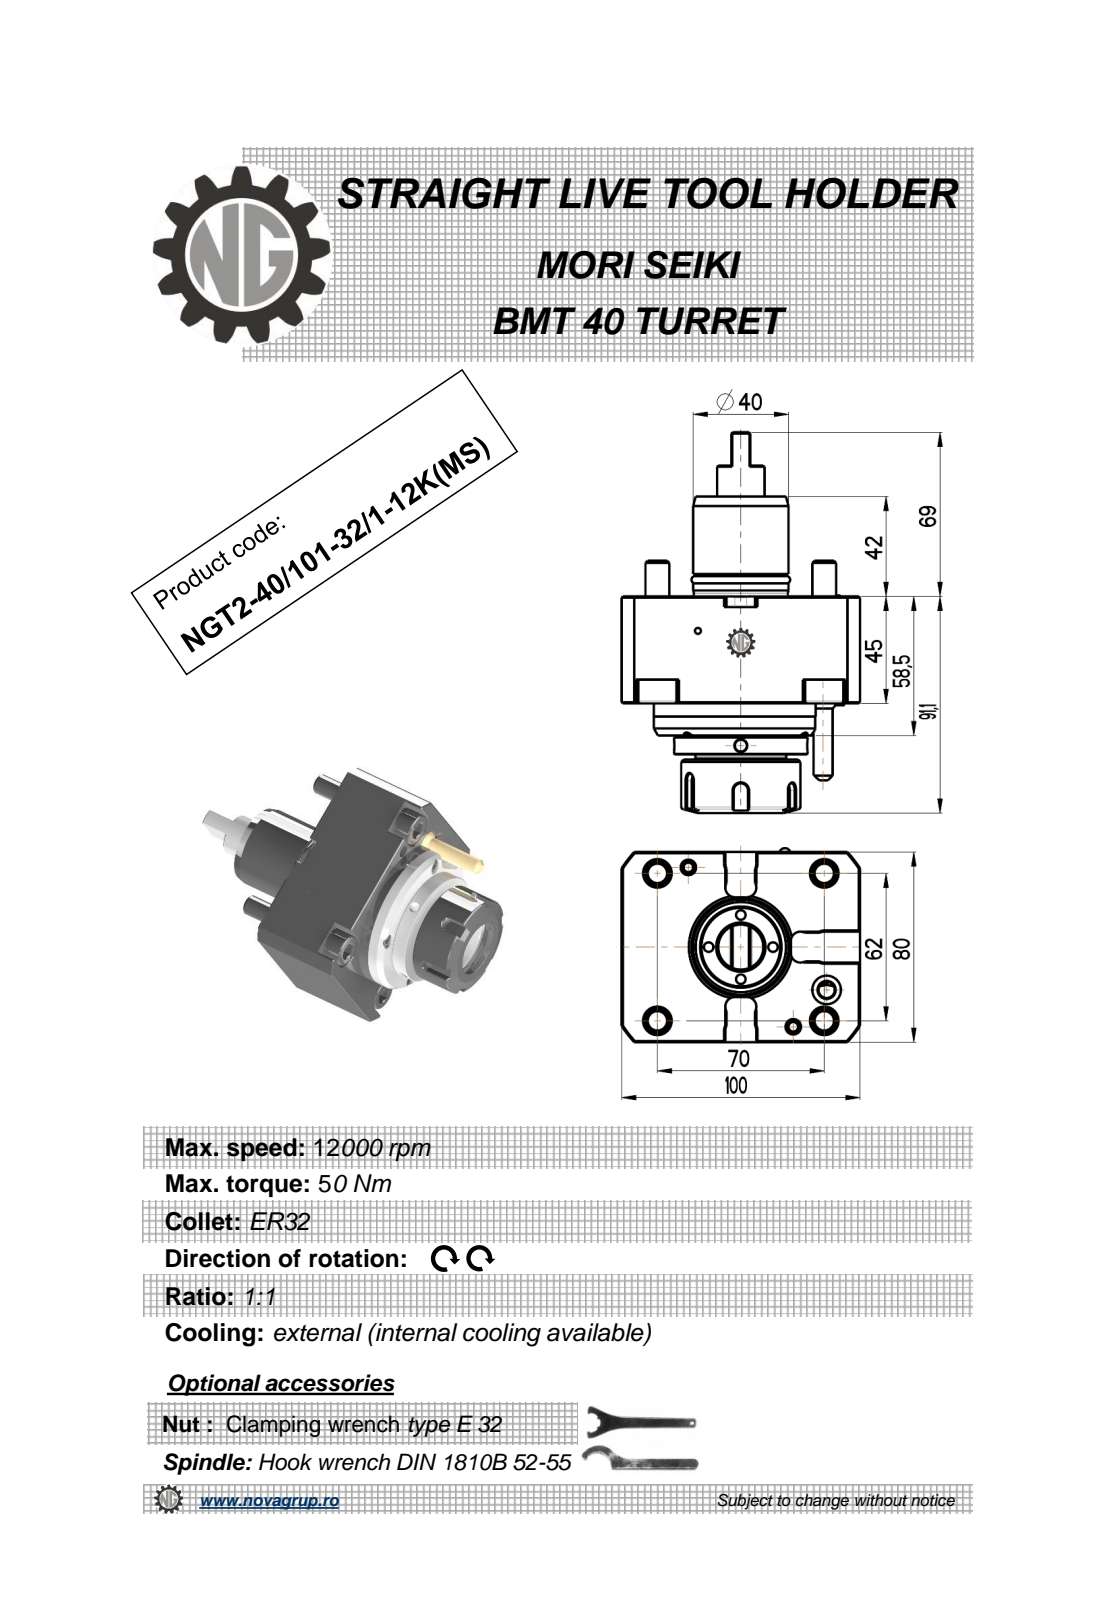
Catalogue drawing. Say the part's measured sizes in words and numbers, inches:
The part is named "NGT2_40_101_32_1_12K_MS". Its 3-D file was written by "PRO/ENGINEER BY PARAMETRIC TECHNOLOGY CORPORATION, 2010280 (CONFIG_CONTROL_DESIGN)". It is 1 solid with 392 faces: 155 planar, 106 cylindrical and 131 other. Overall it measures 6.303 by 3.937 by 3.213 inches. Its volume is 32.28 cubic inches and its surface area 90.09 square inches. Round holes: 3 of diameter 0.197, 1 of diameter 0.118, 1 of diameter 0.268, 1 of diameter 1.063. Round bosses or shafts: 4 of diameter 0.63, 4 of diameter 0.394, 1 of diameter 2.874, 1 of diameter 2.205, 1 of diameter 1.969, 1 of diameter 1.732, 1 of diameter 1.575, 1 of diameter 1.476. Partial cylindrical surfaces (rounded edges, fillets, slot ends): 12 of radius 0.157, 7 of radius 0.236, 6 of radius 0.009, 5 of radius 0.118, 4 of radius 0.335, 2 of radius 0.031, 1 of radius 0.697, 1 of radius 0.776. The main face-to-face distances are 3.15, 1.772, 3.937, 2.303, 0.531, 0.177, 3.409, 0.315, 0.02, 1.594. The hole center spacings are 0.187, 1.459, 1.585.
